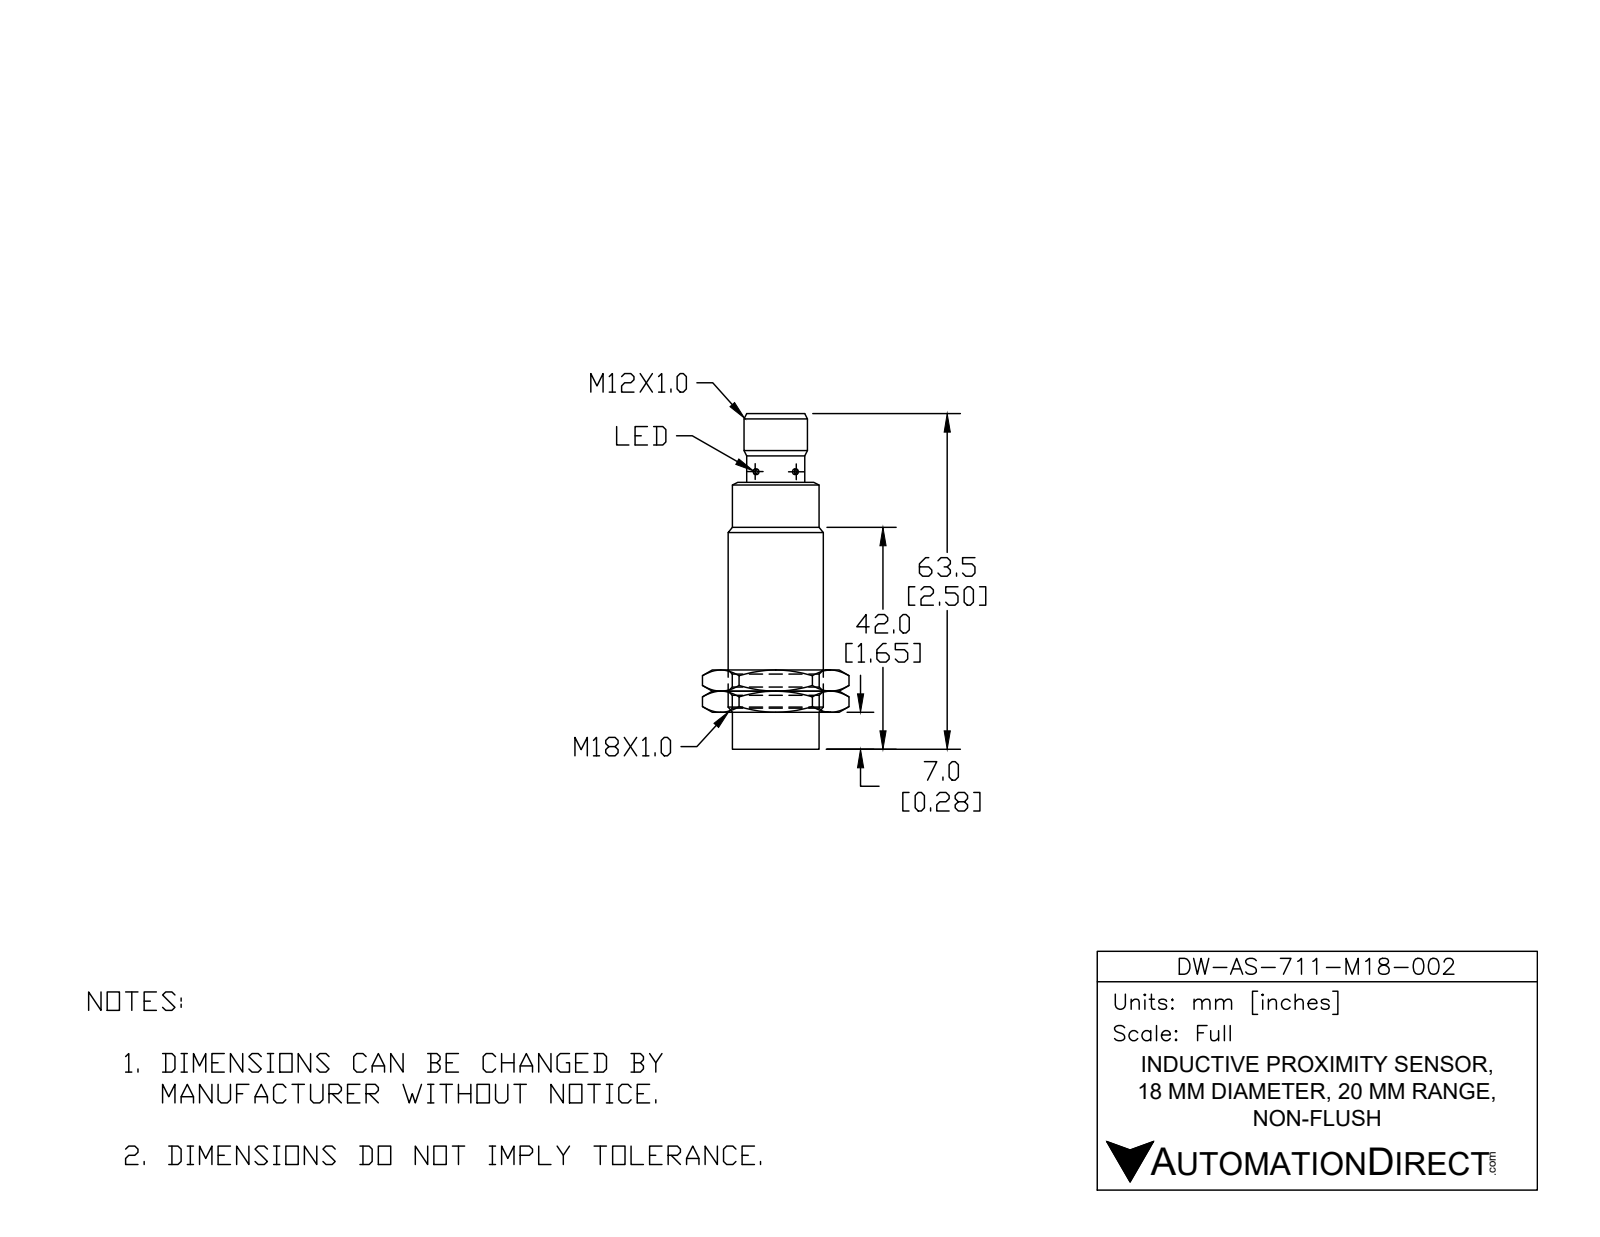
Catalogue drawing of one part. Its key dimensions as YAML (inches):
part_name: "DW-AS-712-M18-002"
step_written_by: "SolidWorks 2017 (AUTOMOTIVE_DESIGN)"
units: inches
bodies: {solids: 1, faces: 40, planar: 8, cylindrical: 17, other: 15}
overall_size: [2.5, 0.709, 0.709]
volume: 0.778
surface_area: 6.608
round_holes:
  - {diameter: 0.118, count: 2}
  - {diameter: 0.335, count: 1}
round_bosses_or_shafts:
  - {diameter: 0.04, count: 4}
  - {diameter: 0.709, count: 1}
  - {diameter: 0.646, count: 1}
  - {diameter: 0.459, count: 1}
  - {diameter: 0.415, count: 1}
partial_cylinders:
  - {radius: 0.02, count: 2}
face_to_face_distances: [2.157, 1.988, 0.169, 2.5, 0.512, 0.343, 0.276, 1.713, 1.882, 2.224]
